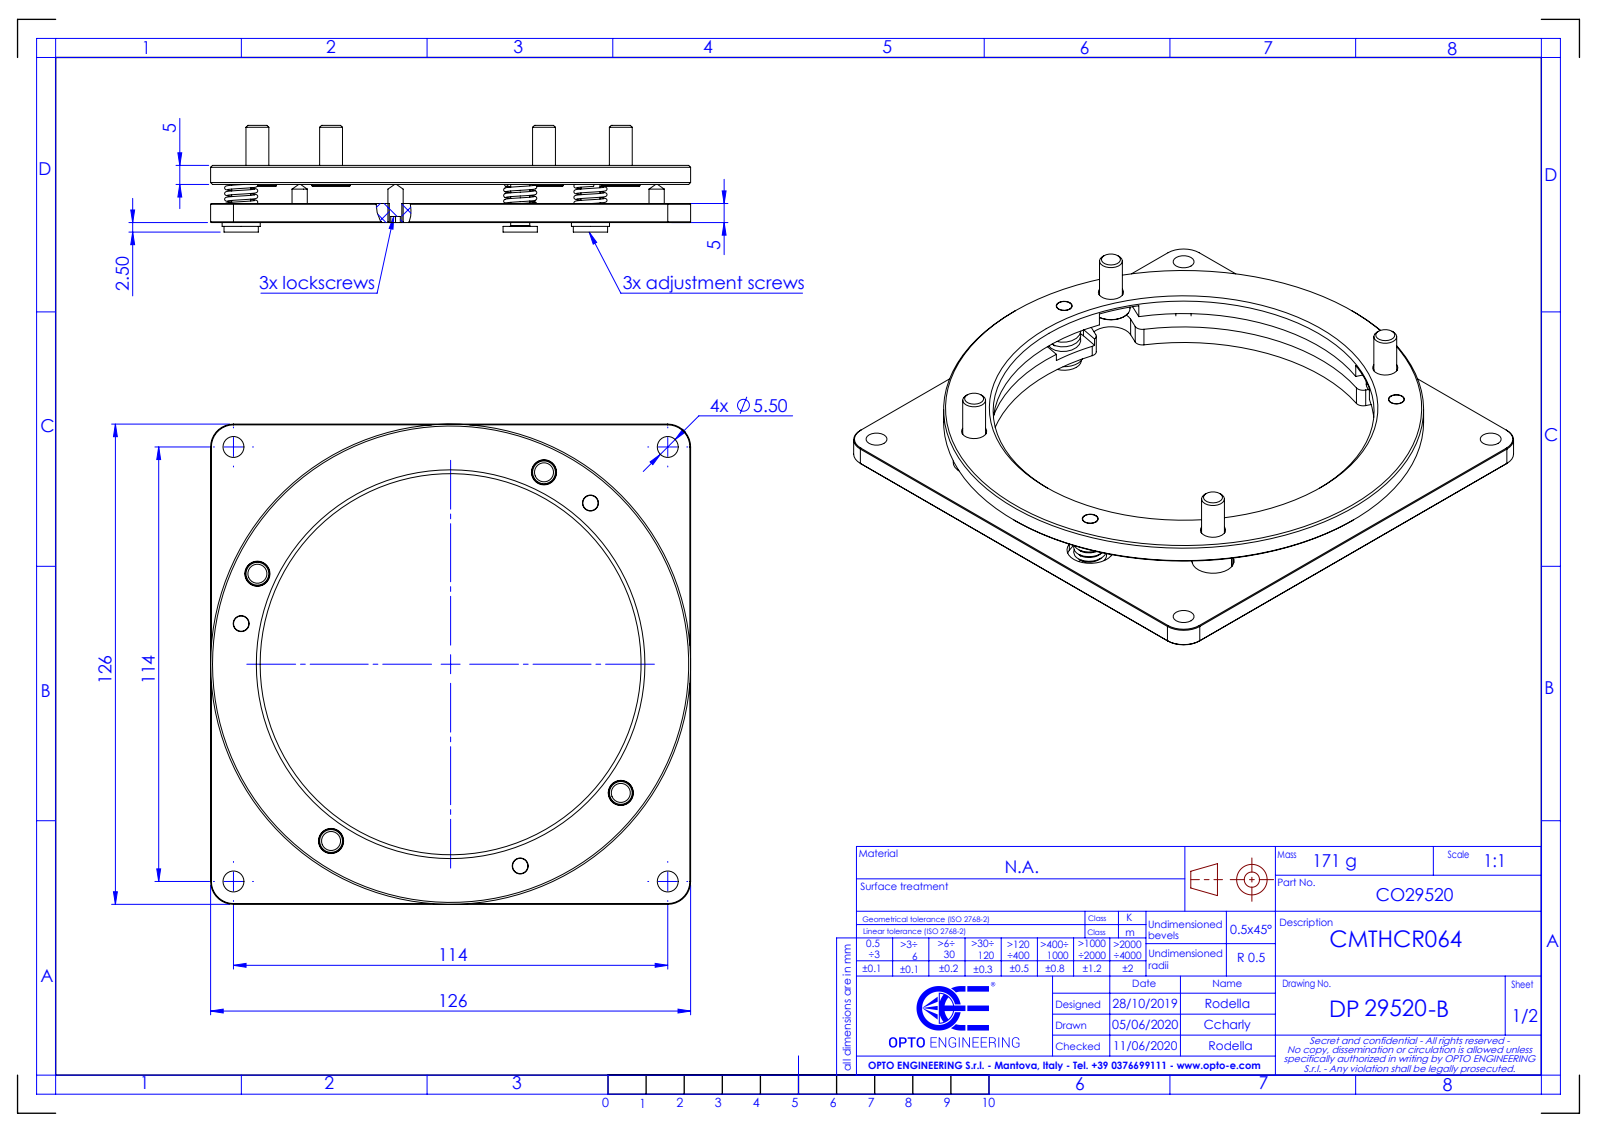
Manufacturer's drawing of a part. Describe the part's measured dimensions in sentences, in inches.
The part is named "DP29520". Its 3-D file was written by "SolidWorks 2021 (CONFIG_CONTROL_DESIGN)". It is 0 solids with 267 faces: 117 planar, 102 cylindrical and 48 other. Overall it measures 4.961 by 4.961 by 1.102 inches. Round holes: 4 of diameter 0.217, 4 of diameter 0.26, 3 of diameter 0.165, 1 of diameter 3.937, 1 of diameter 4.016. Round bosses or shafts: 7 of diameter 0.394, 4 of diameter 0.236, 3 of diameter 0.354, 3 of diameter 0.197, 3 of diameter 0.157, 1 of diameter 4.961. Partial cylindrical surfaces (rounded edges, fillets, slot ends): 8 of radius 0.079, 4 of radius 0.217, 4 of radius 0.236, 3 of radius 0.24. The main face-to-face distances are 0.197, 0.394, 0.591, 4.961, 0.413, 0.472, 0.059, 0.63, 0.157, 0.217. The hole center spacings are 2.205, 3.174, 4.488, 3.819, 6.347, 0.542, 0.576, 0.987.
